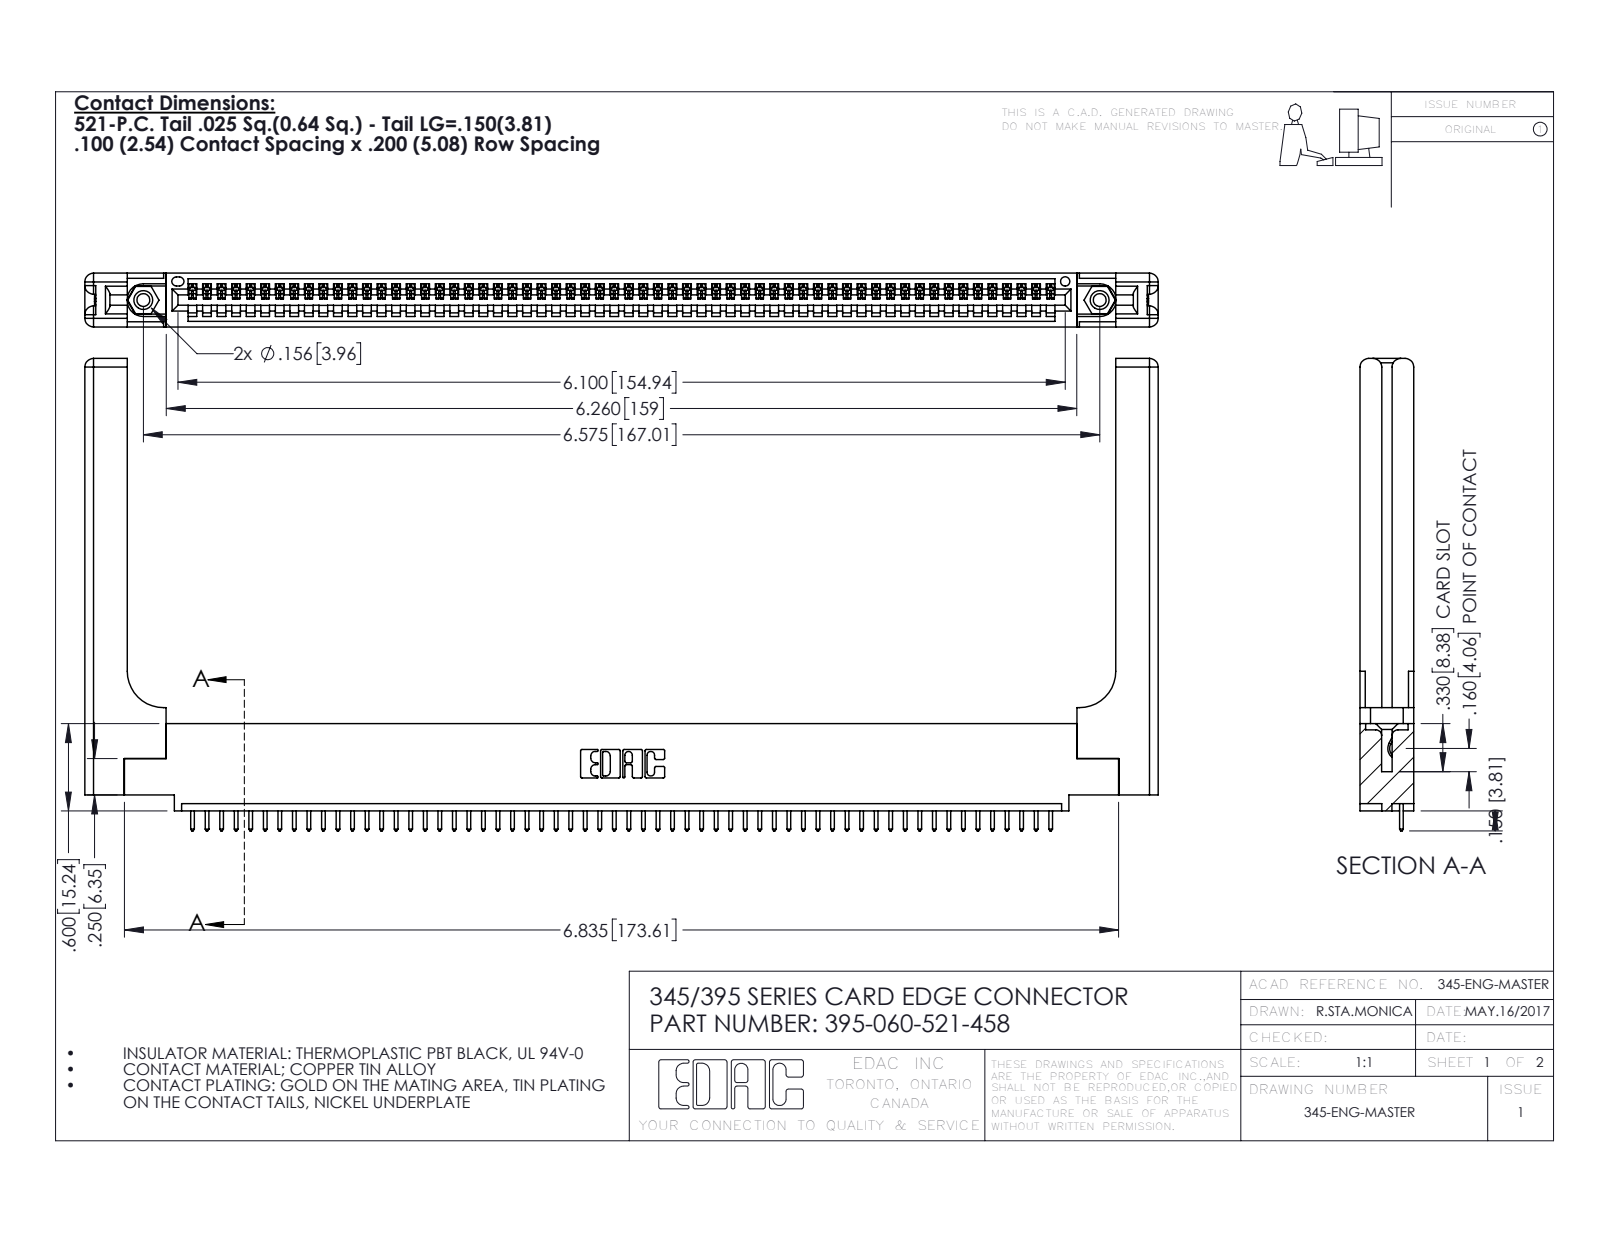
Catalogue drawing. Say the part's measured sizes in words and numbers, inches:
The part is named "345 Part_0.110 Offset - 0.156 Dia-TH; 345-292-001_345-293-121; 345-250-001_345-250-001-102; 395-060-521-458 (+1 more)". Its 3-D file was written by "SolidWorks 2016 (CONFIG_CONTROL_DESIGN)". It is 65 solids with 3866 faces: 2632 planar, 1174 cylindrical and 60 other. Overall it measures 7.379 by 3.247 by 0.37 inches. Its volume is 1.599 cubic inches and its surface area 44.16 square inches. Round holes: 2 of diameter 0.089, 2 of diameter 0.125, 2 of diameter 0.156, 1 of diameter 0.064. Round bosses or shafts: 2 of diameter 0.155. Partial cylindrical surfaces (rounded edges, fillets, slot ends): 120 of radius 0.006, 120 of radius 0.01, 22 of radius 0.01, 16 of radius 0.06, 6 of radius 0.007, 6 of radius 0.031, 3 of radius 0.026, 2 of radius 0.03. The main face-to-face distances are 0.072, 0.37, 0.298, 0.098, 0.272, 0.025, 0.2, 0.225, 0.148, 0.15. The hole center spacings are 0.27, 6.339, 6.575.
